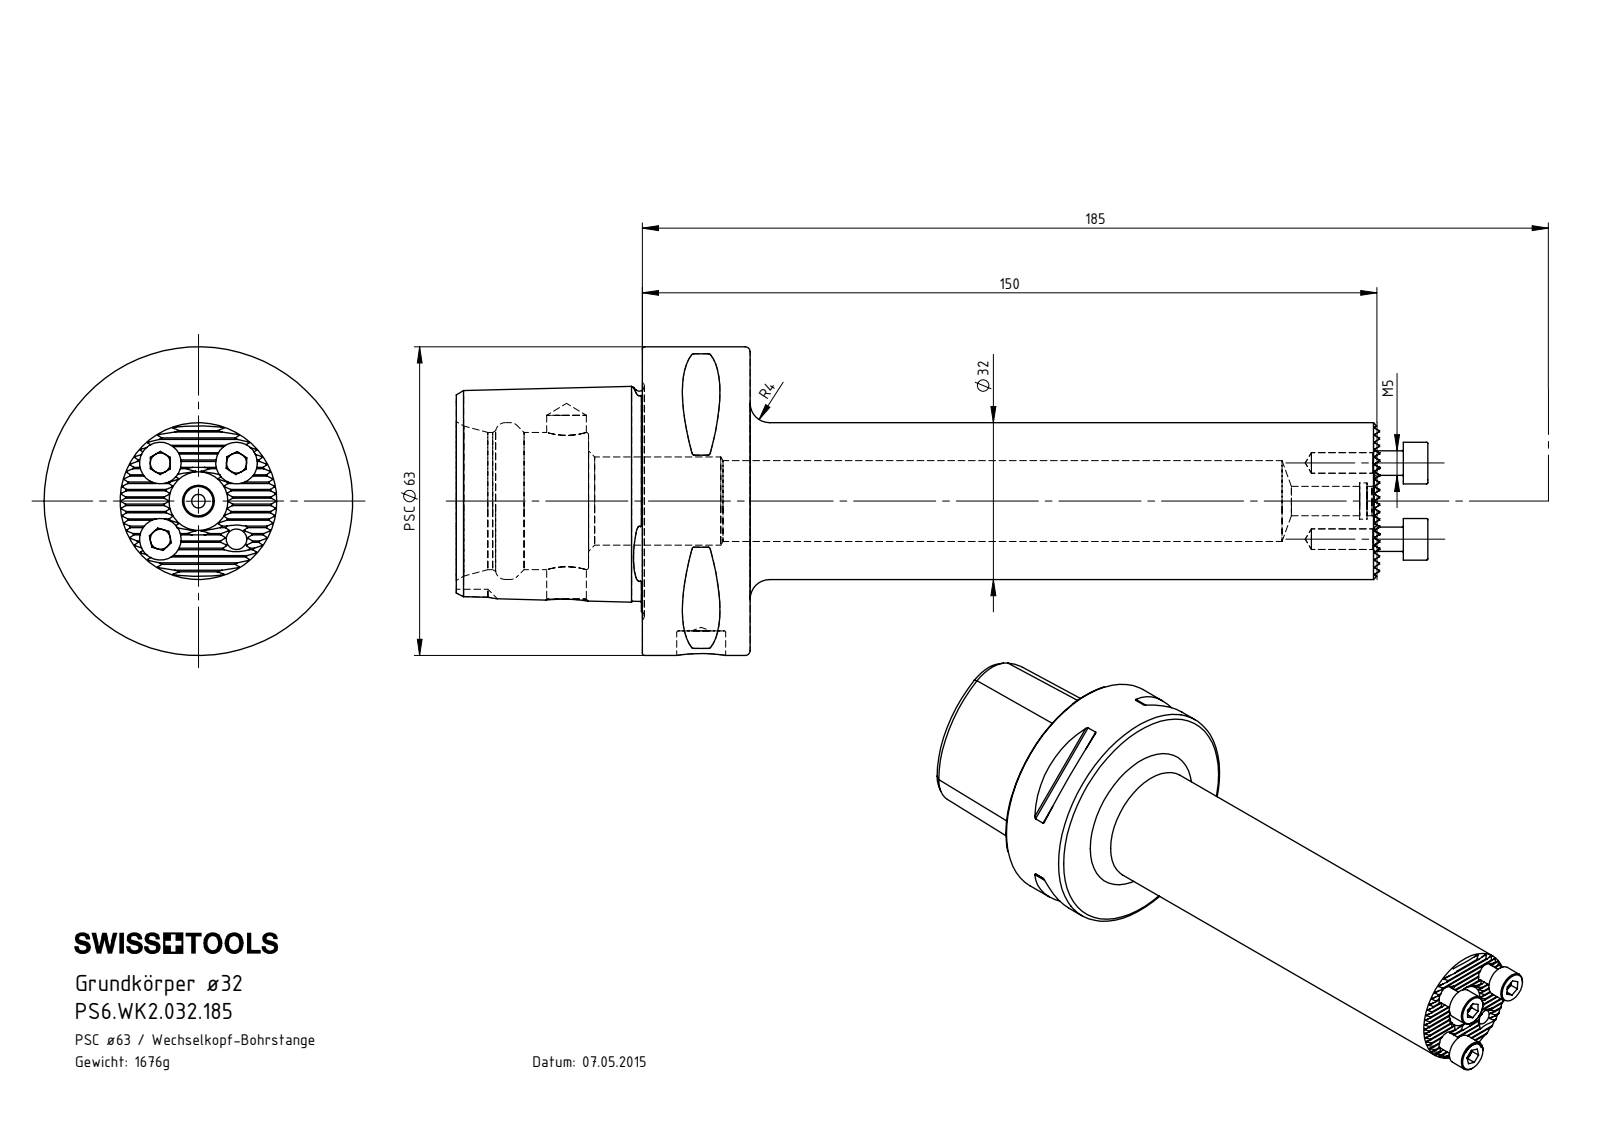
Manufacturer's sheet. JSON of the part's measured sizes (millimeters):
{"part_name": "DIN 3771 - 6x1; ISO 4762 - M5 x 14; PS6.WK2.032.185; WK1-ER1.016.112_A_Fertigbearbeitung (+2 more)", "step_written_by": "SolidWorks 2017 (AUTOMOTIVE_DESIGN)", "units": "millimeters", "bodies": {"solids": 7, "faces": 353, "planar": 201, "cylindrical": 77, "other": 75}, "overall_size": [198.4, 63, 63], "volume_mm3": 196804, "surface_area_mm2": 48962, "round_holes": [[4.2, 4], [3, 1], [4, 1], [6, 1], [7.4, 1], [8.1, 1], [16.5, 1], [18, 1], [28, 1], [32, 1]], "round_bosses_or_shafts": [[8.5, 3], [5, 3], [63, 1], [16, 1]], "partial_cylinders_radius": [[0.12, 21], [0.5, 8], [6, 1]], "face_to_face_distances": [22, 1.3, 2.6, 38, 60, 3.9, 167.1, 129.1, 107.1, 5.2], "hole_center_spacings": [11, 15.56, 22.01, 27.5]}
